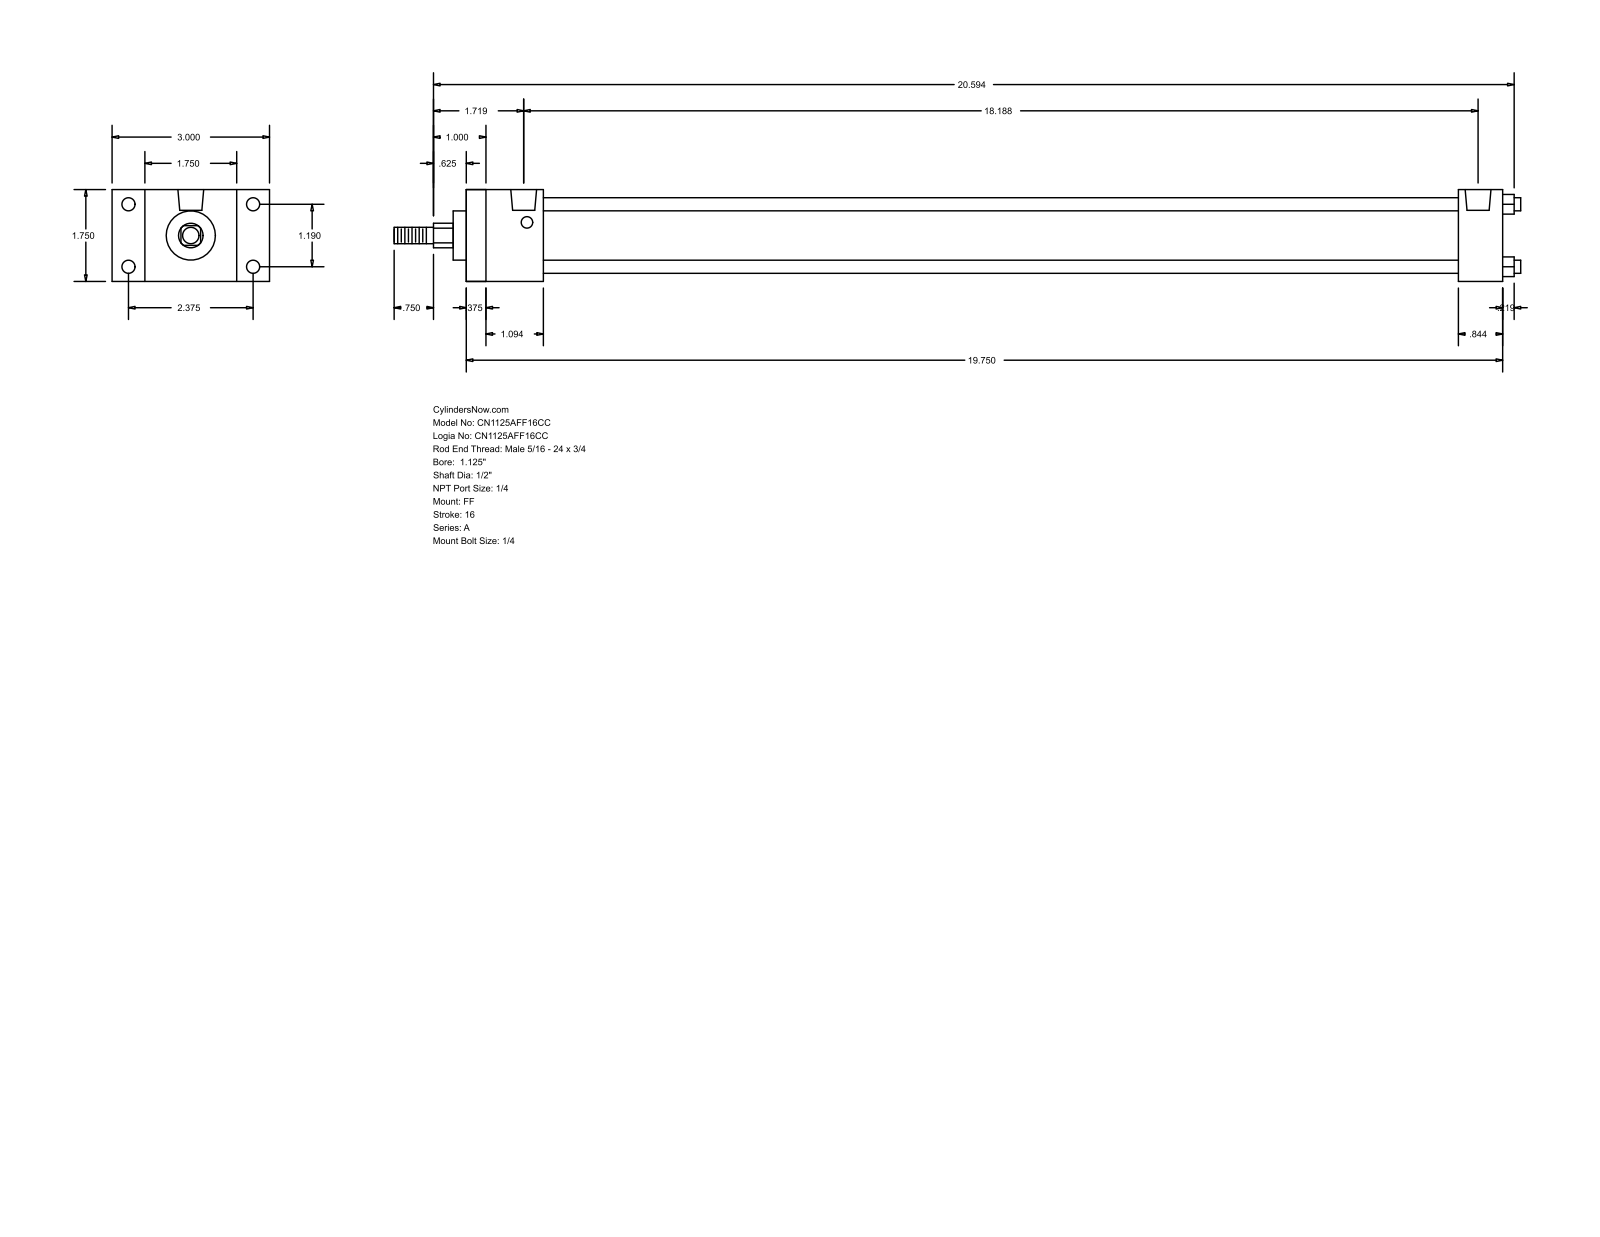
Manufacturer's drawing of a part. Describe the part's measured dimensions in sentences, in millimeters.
The part is named "A_FF__0112_0.5". Its 3-D file was written by "GSSL Pune (CONFIG_CONTROL_DESIGN)". It is 0 solids with 92 faces: 64 planar, 28 cylindrical and 0 other. Overall it measures 545.31 by 76.2 by 44.45 millimeters. Round holes: 4 of diameter 5.56, 4 of diameter 6.35, 2 of diameter 12.49. Round bosses or shafts: 4 of diameter 6.35, 1 of diameter 31.88, 1 of diameter 23.81, 1 of diameter 12.7, 1 of diameter 7.94. Partial cylindrical surfaces (rounded edges, fillets, slot ends): 1 of radius 5.94. The main face-to-face distances are 44.46, 501.64, 9.52, 492.12, 15.87, 480.21, 470.69, 21.43, 37.3, 27.78. The hole center spacings are 30.22, 60.32, 67.47, 458.79, 1.58, 1.59, 460.37, 460.38.
